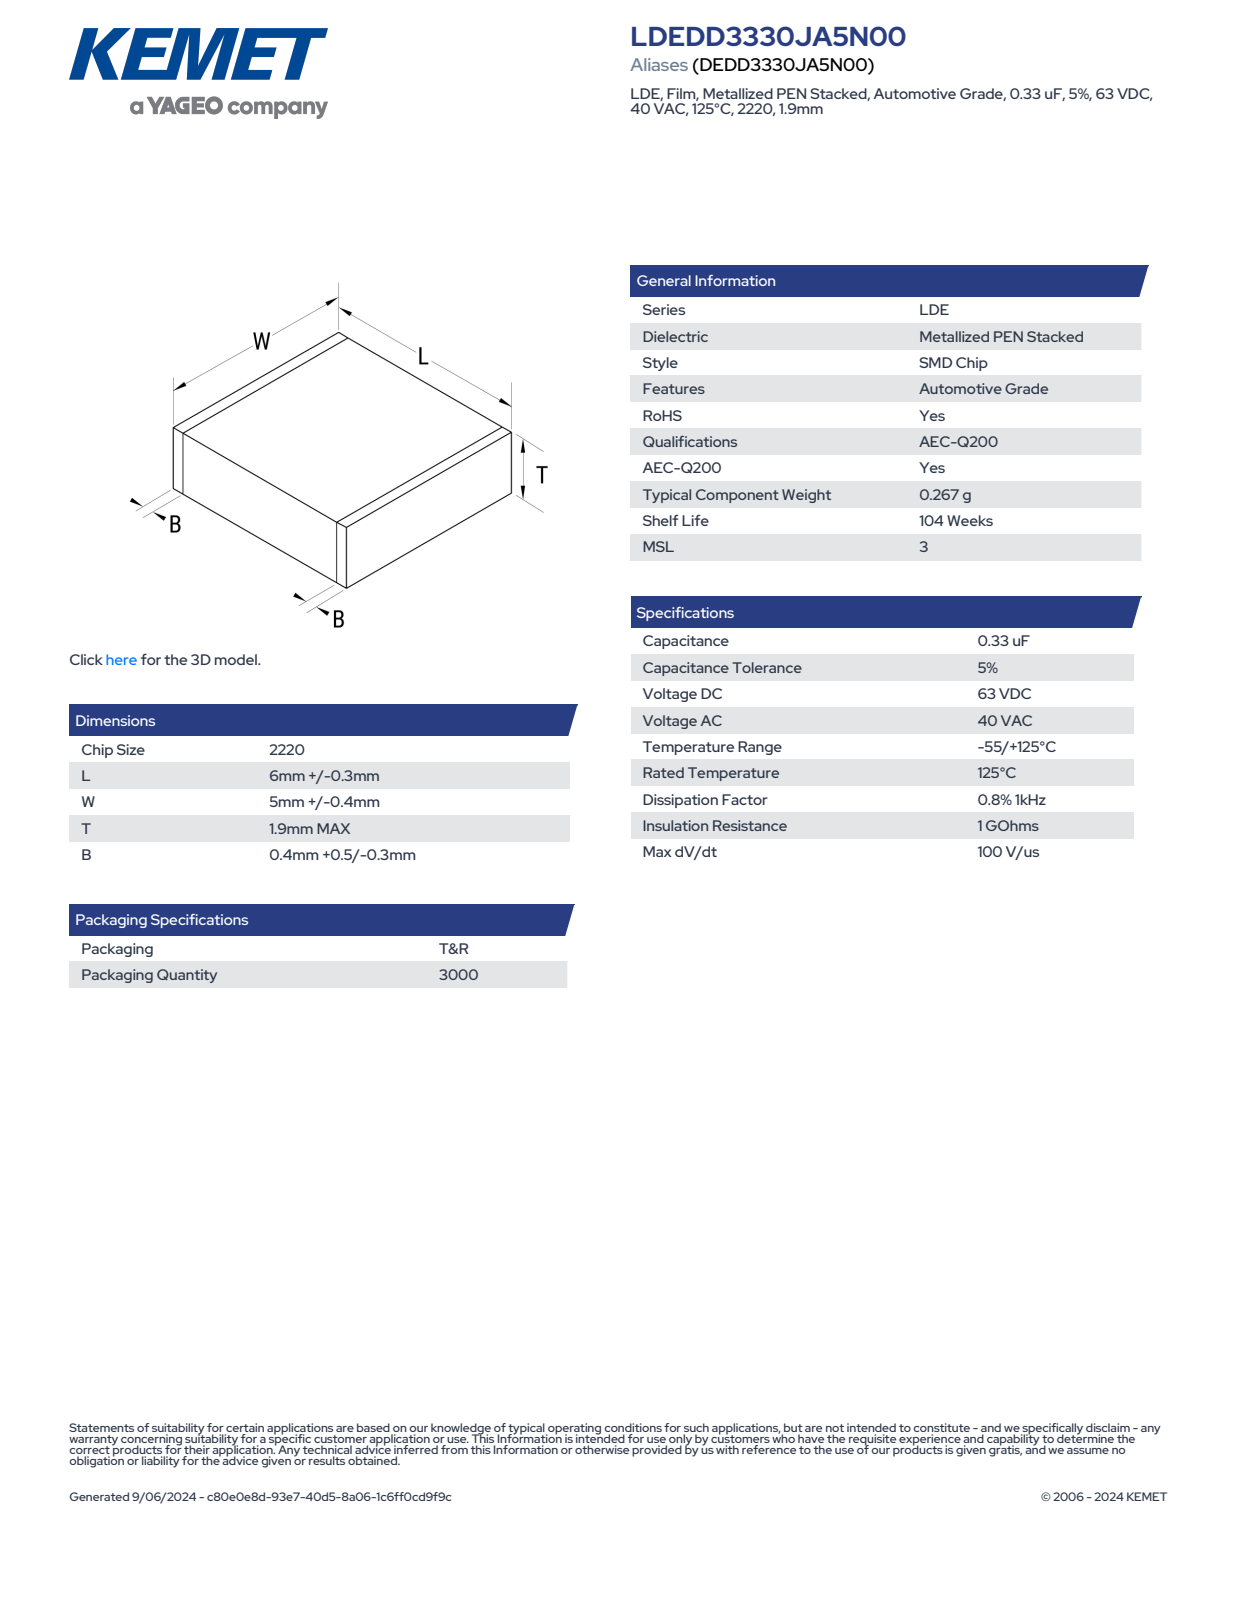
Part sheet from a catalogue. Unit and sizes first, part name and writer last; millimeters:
Units: millimetres
Overall size (bounding box): 6.3 × 5.4 × 1.9
Main face-to-face distances: 1.88, 1.89, 6.3, 5.38, 1.9, 5.39, 5.4, 0.5, 5.8, 5.3
Volume: 64 mm³ · Surface area: 114 mm²
Bodies: 4 solids, 73 faces (73 planar, 0 cylindrical, 0 other)
Part name (STEP PRODUCT): CFS_LDELDB_2220_L6.3W5.4T1.9B0.9
STEP written by: SolidWorks 2020 (AUTOMOTIVE_DESIGN)
